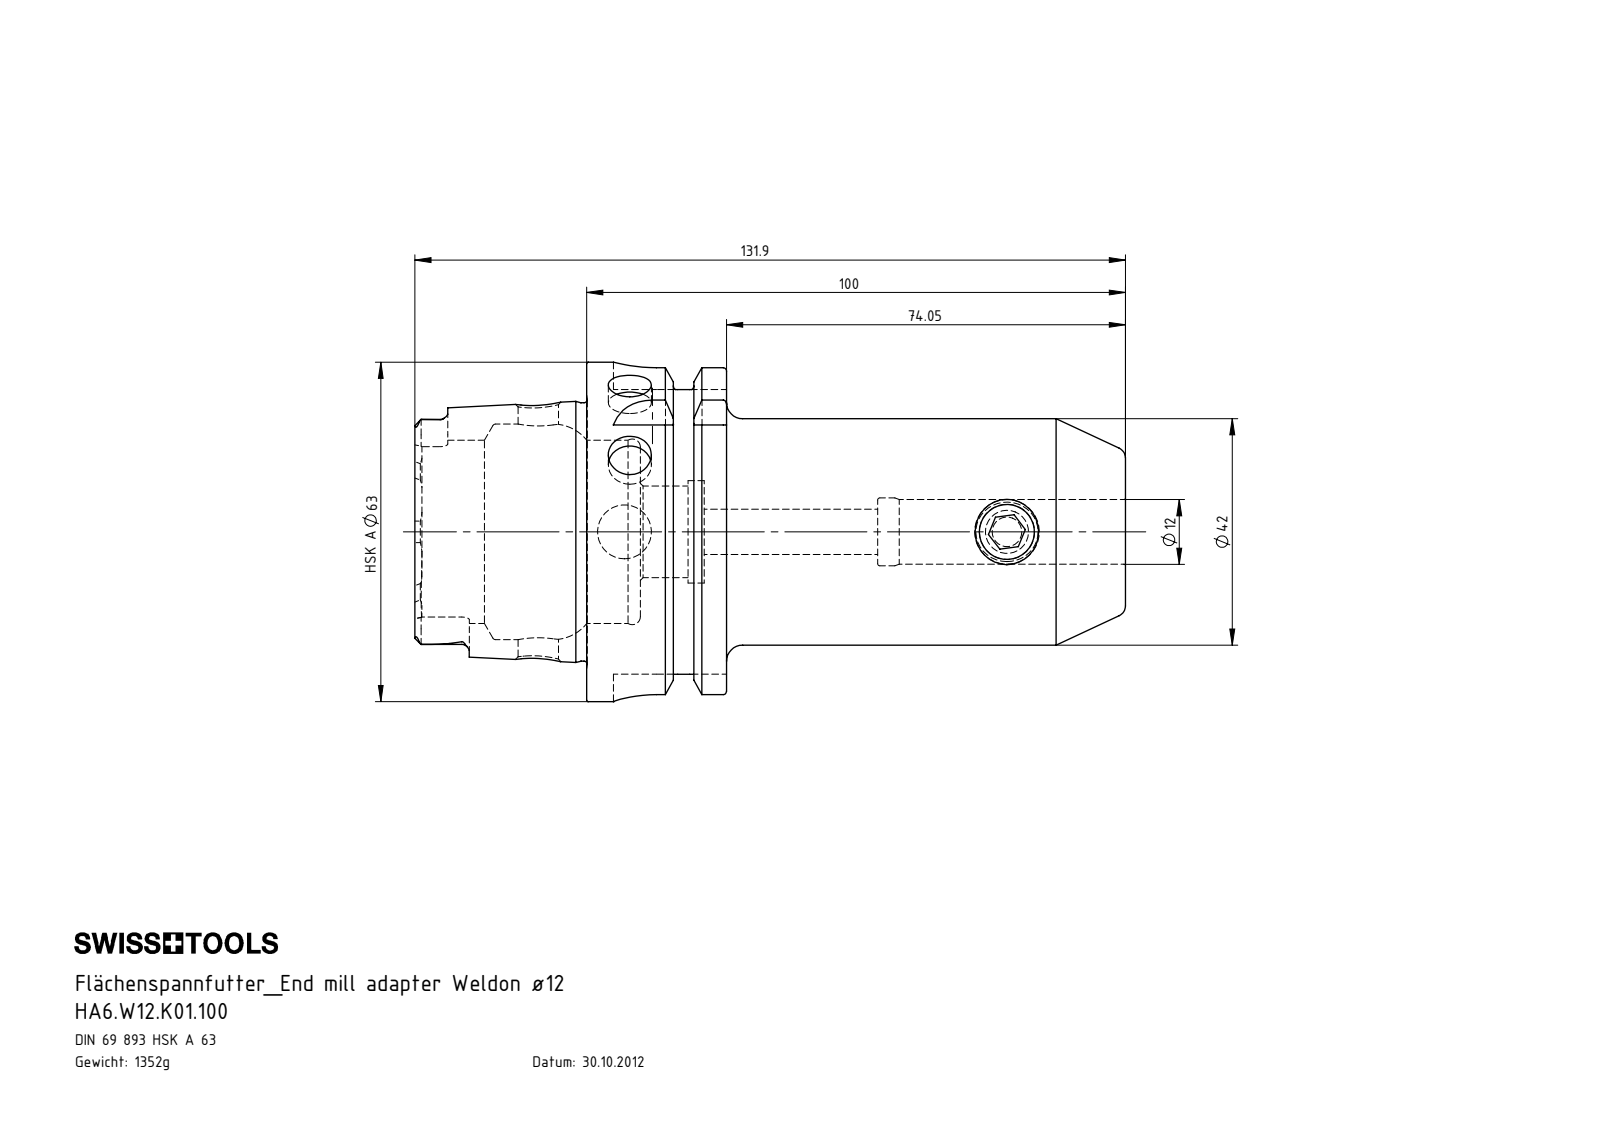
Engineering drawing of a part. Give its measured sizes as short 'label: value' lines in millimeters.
name: HA6-W12.K01.100; W12-ER1.001.016; HA6-W12.K01.100_A_Fertigbearbeitung
written by: SolidWorks 2012 (CONFIG_CONTROL_DESIGN)
unit: mm
bodies: 2 solids, 208 faces (58 planar, 57 cylindrical, 93 other)
size: 131.9 × 63 × 63
volume: 172 241 mm³; area: 35 020 mm²
holes: 2× ⌀8, 1× ⌀7.5, 1× ⌀8.4, 1× ⌀10, 1× ⌀10.25, 1× ⌀12, 1× ⌀12.6, 1× ⌀17, 1× ⌀19, 1× ⌀34, 1× ⌀40
bosses: 1× ⌀63, 1× ⌀54.95, 1× ⌀47.94, 1× ⌀42, 1× ⌀12
rounds: 6× R1.4, 4× R2.88, 4× R8
face distances: 25.95, 16, 9.95, 100, 90.05, 74.05, 31.9, 41.85, 57.85, 131.9
hole spacings: 71
